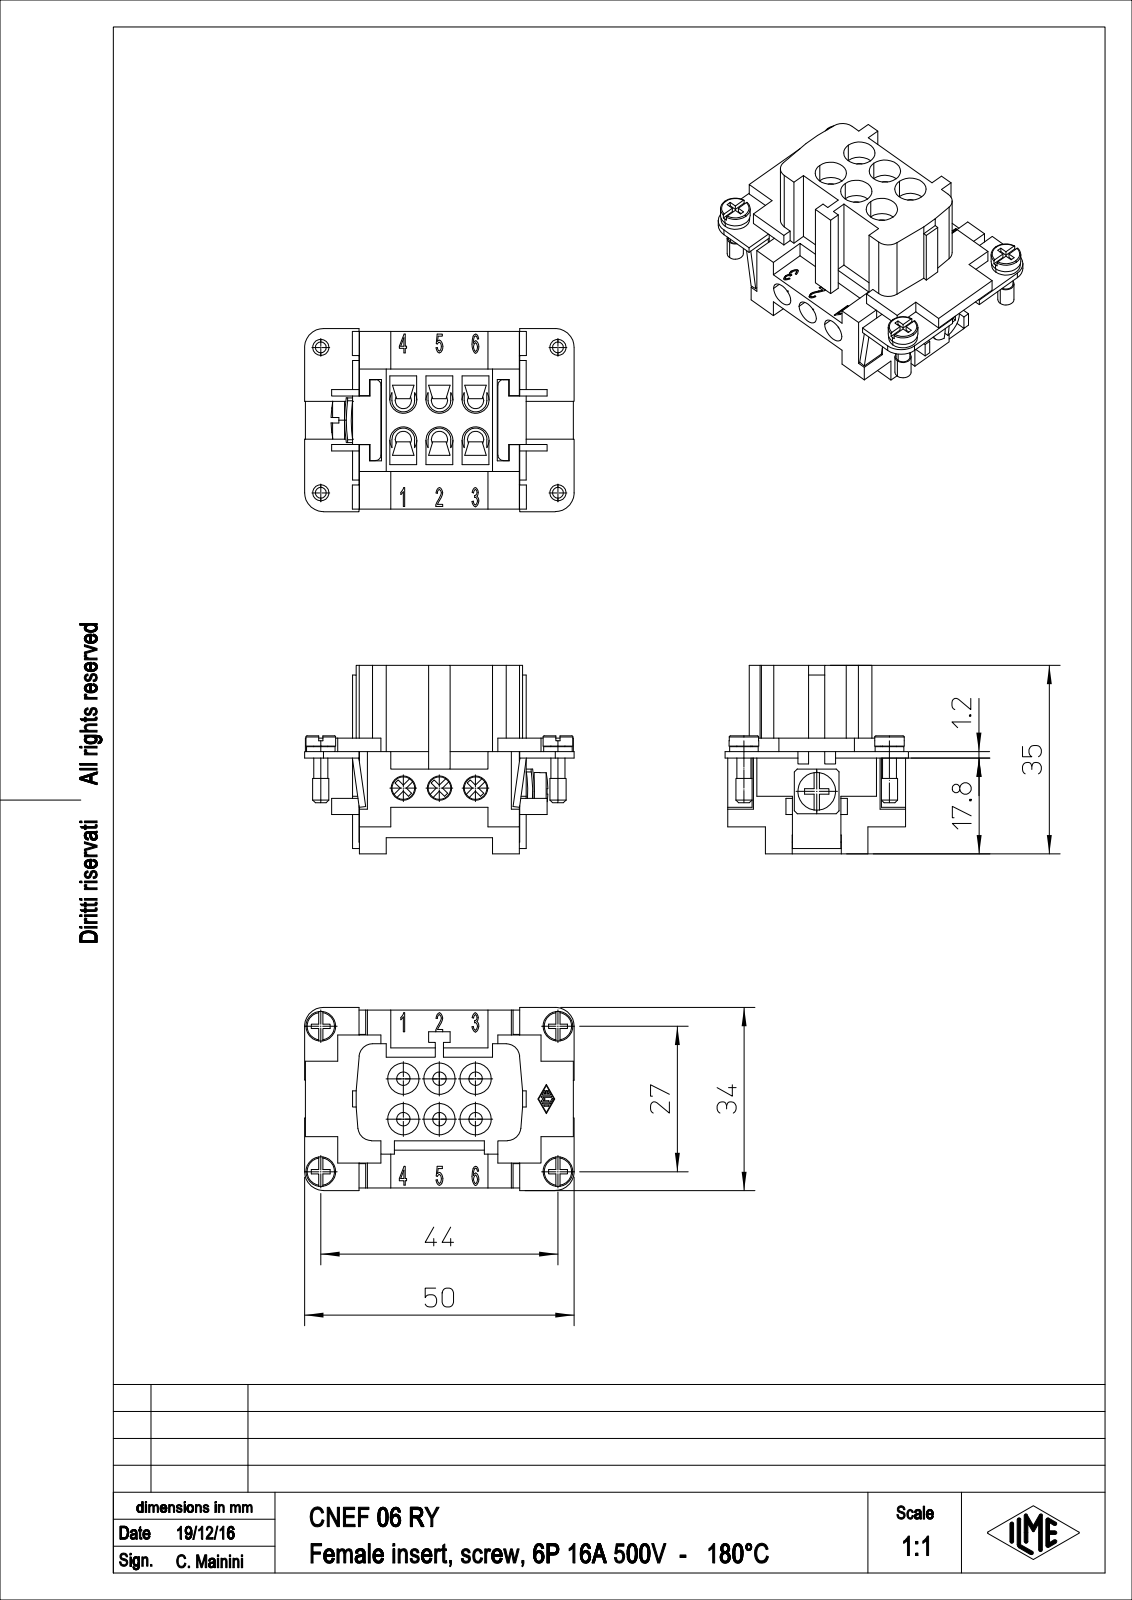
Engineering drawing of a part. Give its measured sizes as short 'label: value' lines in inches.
name: CNEF_06_RY
written by: PTC Creo Elements/Direct Modeling 19.0E 27-Jun-2016 (C) Parametric Technology GmbH (AUTOMOTIVE_DESIGN)
unit: in
bodies: 2 solids, 910 faces (606 planar, 160 cylindrical, 144 other)
size: 1.969 × 1.378 × 1.339
volume: 1.316 in³; area: 24.49 in²
holes: 6× ⌀0.098, 6× ⌀0.118, 6× ⌀0.228, 3× ⌀0.177, 1× ⌀0.128
bosses: 4× ⌀0.217, 4× ⌀0.209, 4× ⌀0.118, 4× ⌀0.102, 3× ⌀0.165, 1× ⌀0.276
rounds: 14× R0.004, 10× R0.098, 6× R0.083, 4× R0.039, 4× R0.138, 1× R0.217
face distances: 0.047, 0.098, 0.049, 0.63, 1.22, 0.197, 0.079, 1.024, 1.219, 0.069
hole spacings: 0.264, 0.528, 0.392, 0.289, 0.387, 0.396, 0.602, 0.283
